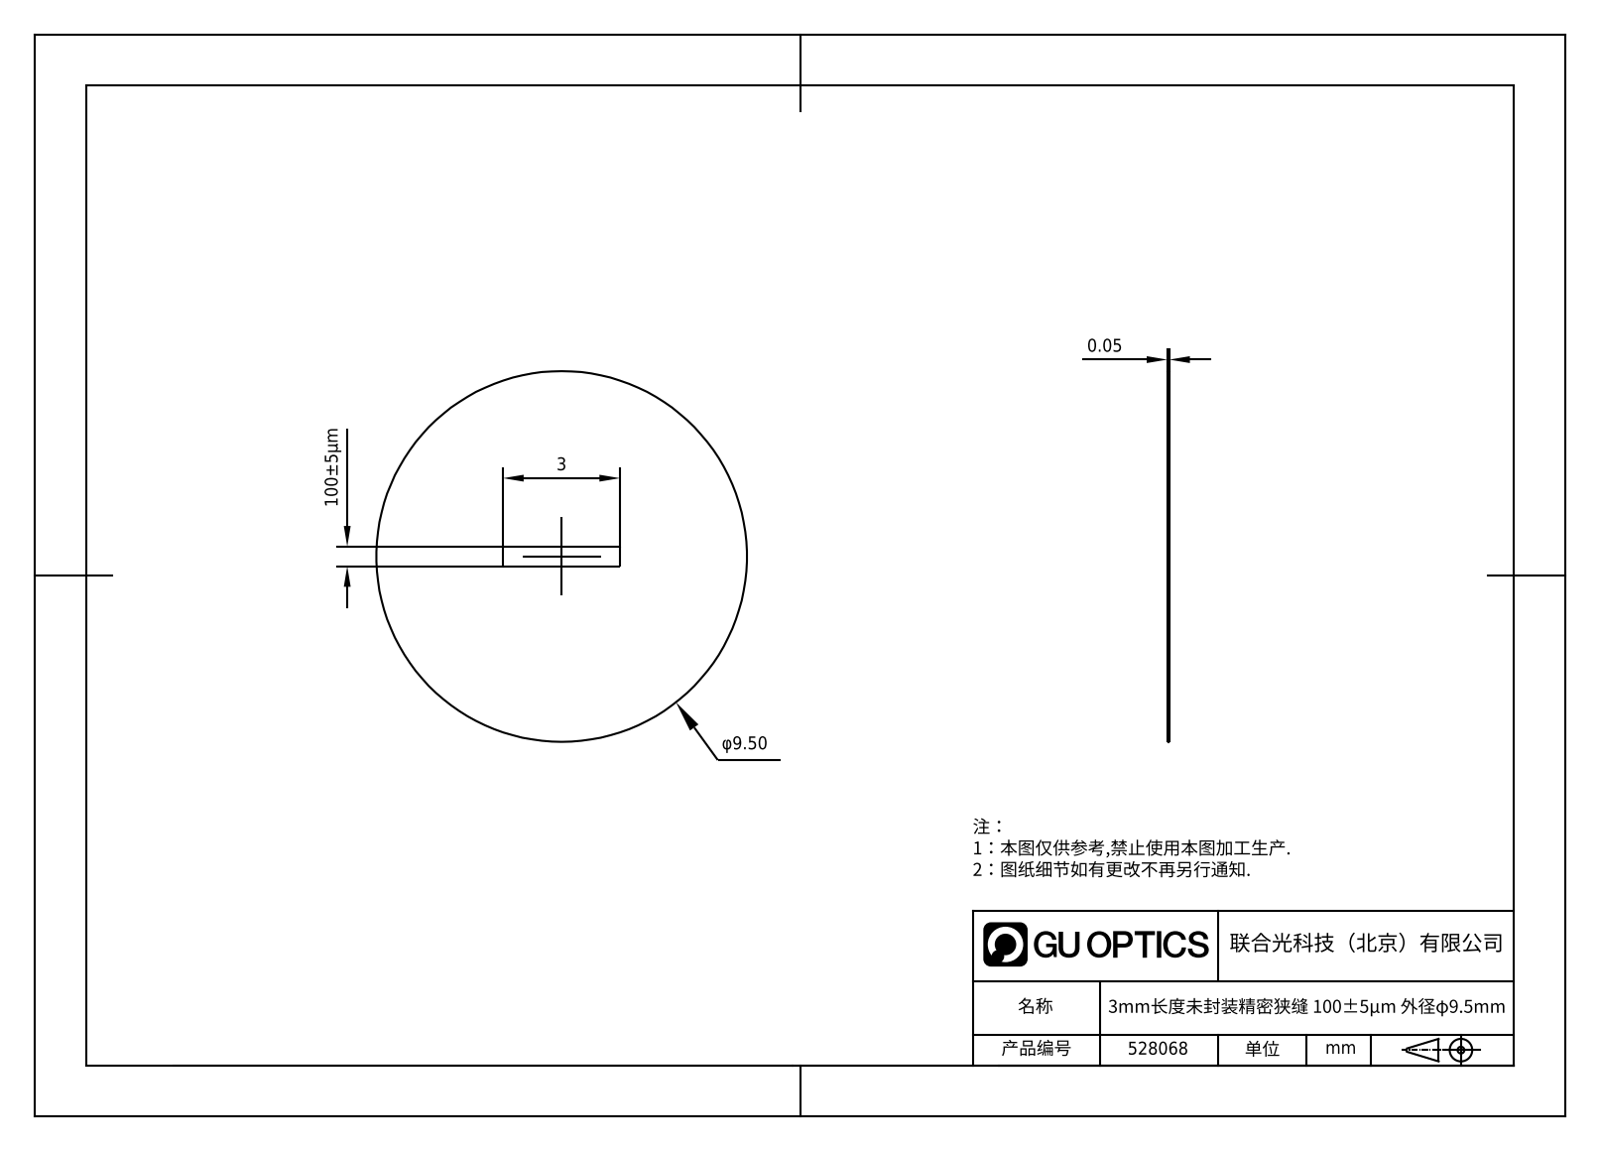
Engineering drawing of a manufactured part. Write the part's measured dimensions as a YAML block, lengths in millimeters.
part_name: "1.5.4.9-ZXG-9.5-100"
step_written_by: "SolidWorks 2021 (CONFIG_CONTROL_DESIGN)"
units: millimeters
bodies: {solids: 1, faces: 8, planar: 6, cylindrical: 2, other: 0}
overall_size: [9.5, 9.5, 0.05]
volume: 4
surface_area: 143
round_bosses_or_shafts:
  - {diameter: 9.5, count: 1}
face_to_face_distances: [3]
